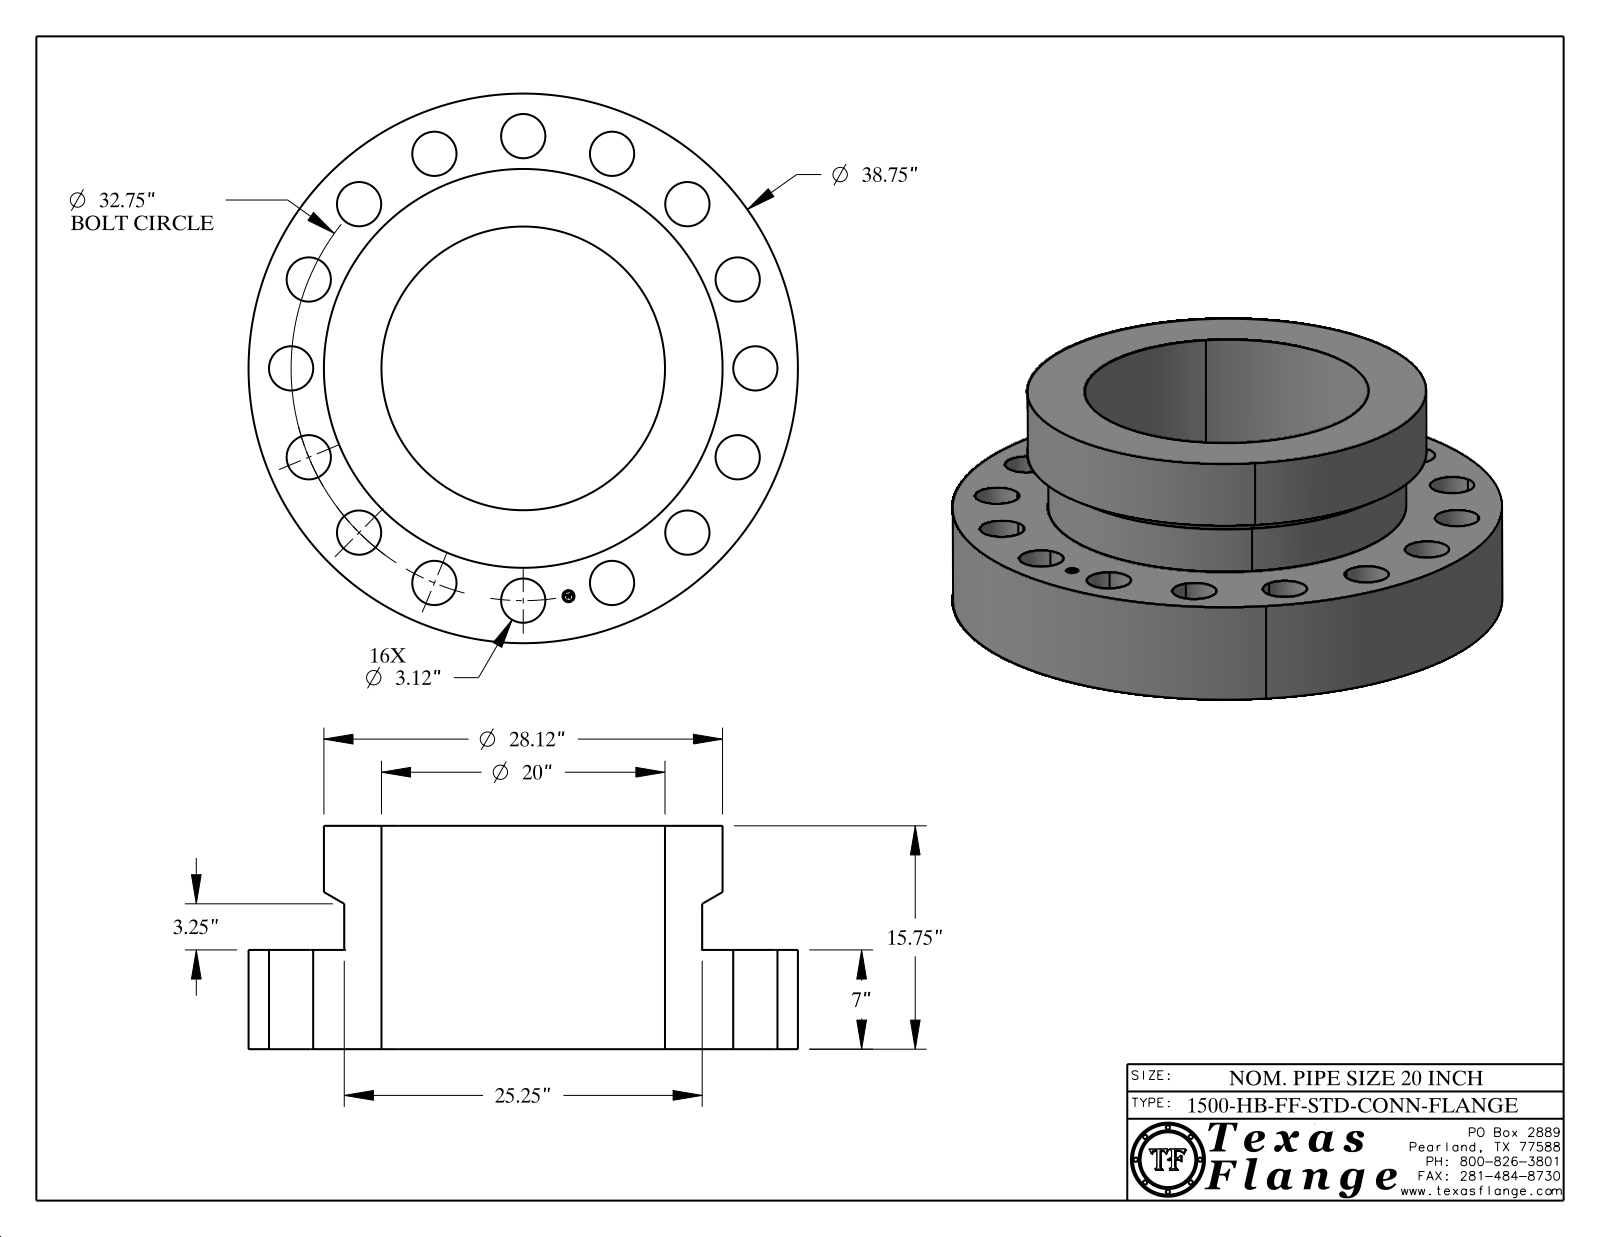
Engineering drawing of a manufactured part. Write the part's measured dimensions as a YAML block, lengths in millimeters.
part_name: "20-1500-HB-FF-STD-CONN-FLANGE"
step_written_by: "CATIA V5 STEP AP214 (AUTOMOTIVE_DESIGN)"
units: millimeters
bodies: {solids: 1, faces: 434, planar: 368, cylindrical: 60, other: 6}
overall_size: [984.3, 984.3, 400.1]
volume: 122000000
surface_area: 3457000
round_holes:
  - {diameter: 79.2, count: 16}
  - {diameter: 21.6, count: 1}
  - {diameter: 508, count: 1}
round_bosses_or_shafts:
  - {diameter: 1.3, count: 8}
  - {diameter: 984.3, count: 1}
  - {diameter: 714.2, count: 1}
  - {diameter: 641.4, count: 1}
  - {diameter: 17, count: 1}
face_to_face_distances: [177.8, 400.1, 222.3, 177.7, 222.4, 6.5, 6.3, 1.2, 4.2, 5.4]
hole_center_spacings: [462.2, 415.9, 318.3, 588.2, 768.5, 162.3, 162.3, 691.6]
